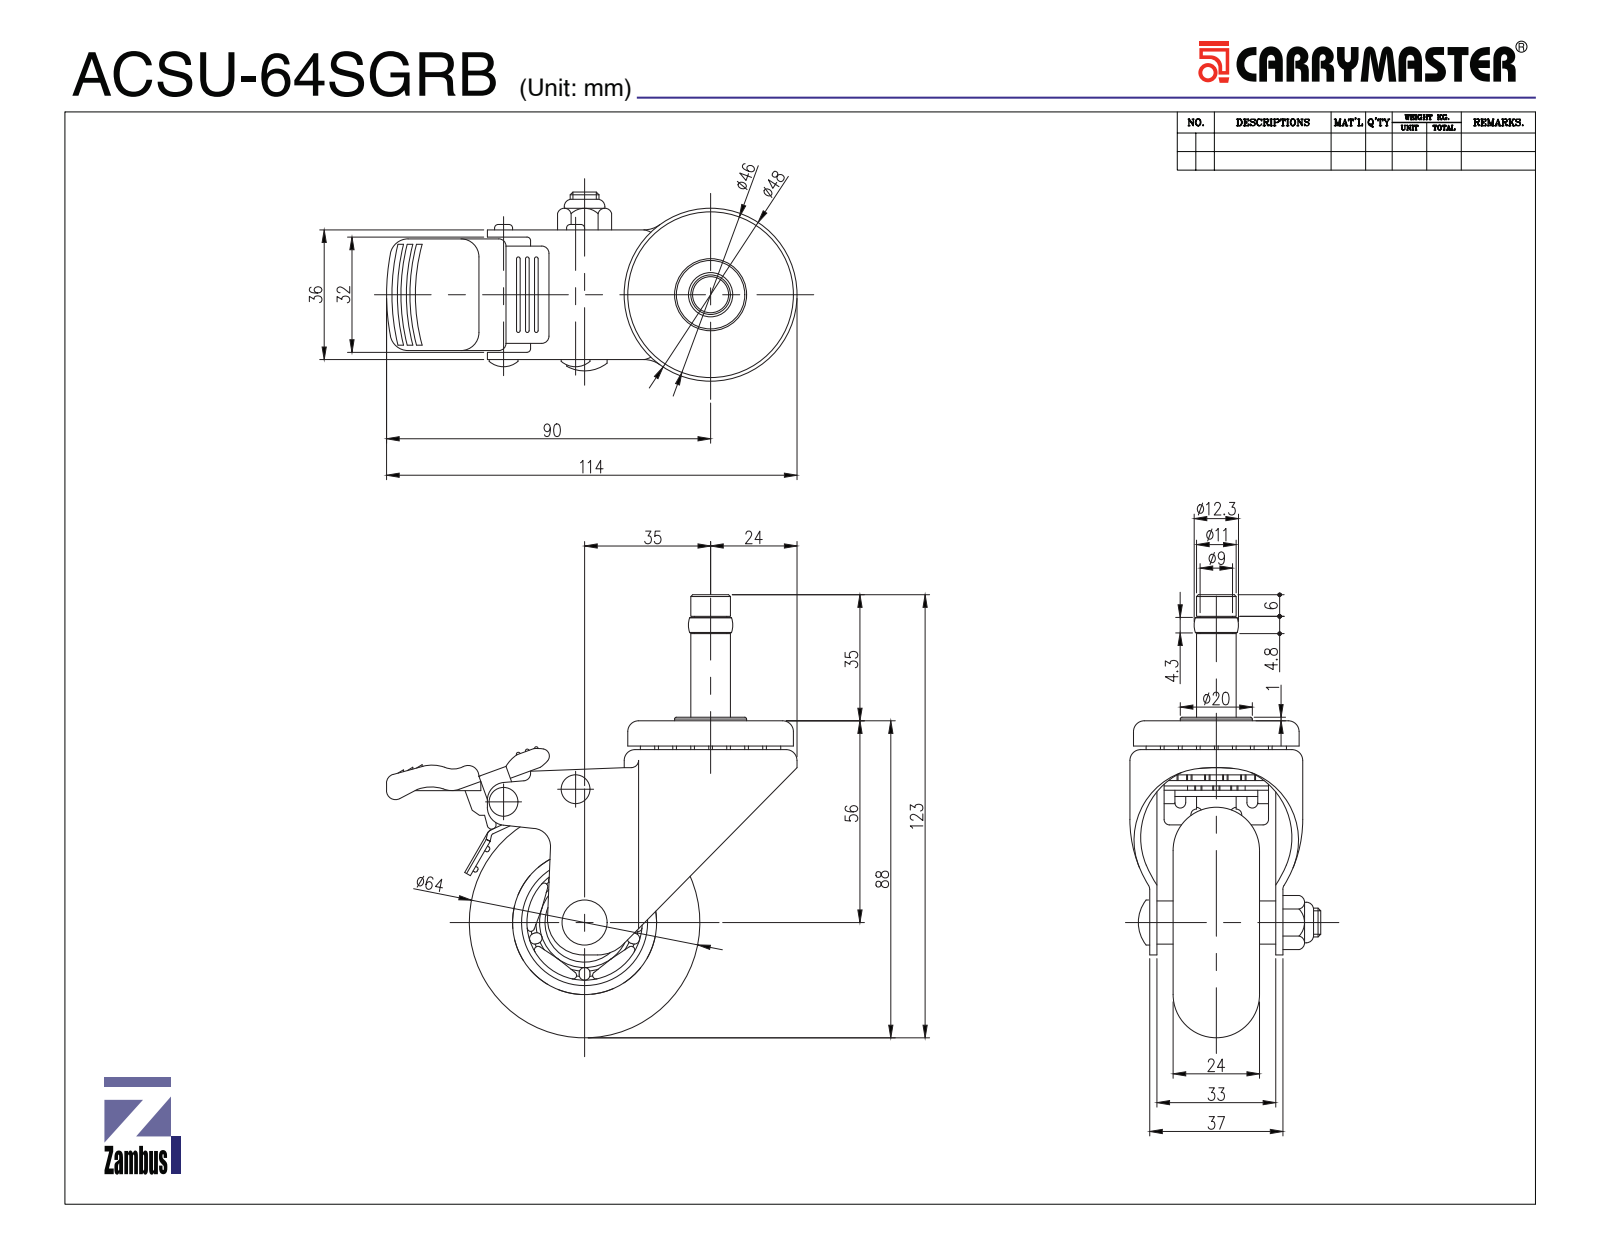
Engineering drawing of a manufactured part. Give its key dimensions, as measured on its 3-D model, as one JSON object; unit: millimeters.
{"part_name": "ACSU-64 URETHANE; KS B 2023 S60 - 608-S-C_KS B 2023 S60 - 608-S-C; 64SSB-FRAME_TOP RING; ACSU-64RF WHEEL PIN (+8 more)", "step_written_by": "SolidWorks 2016 (AUTOMOTIVE_DESIGN)", "units": "millimeters", "bodies": {"solids": 19, "faces": 1069, "planar": 403, "cylindrical": 418, "other": 248}, "overall_size": [123.11, 113.76, 49.2], "volume_mm3": 109123, "surface_area_mm2": 73196, "round_holes": [[3.5, 2], [4, 2], [6.8, 1], [8, 1], [8.1, 1], [10, 1], [11, 1], [17.33, 1], [18.5, 1], [22, 1], [27, 1], [35, 1]], "round_bosses_or_shafts": [[4.9, 2], [47.5, 1], [42.4, 1], [30.3, 1], [20, 1], [18, 1], [16, 1], [12.67, 1]], "partial_cylinders_radius": [[1, 63], [0.75, 44], [1.25, 26], [0.5, 21], [1.5, 13], [2, 12], [8, 8], [2.5, 7]], "face_to_face_distances": [2, 35.5, 3.5, 1.5, 37.5, 1.41, 33.5, 6.75, 30.75, 4.75], "hole_center_spacings": [20.93, 36.67, 40.24]}
